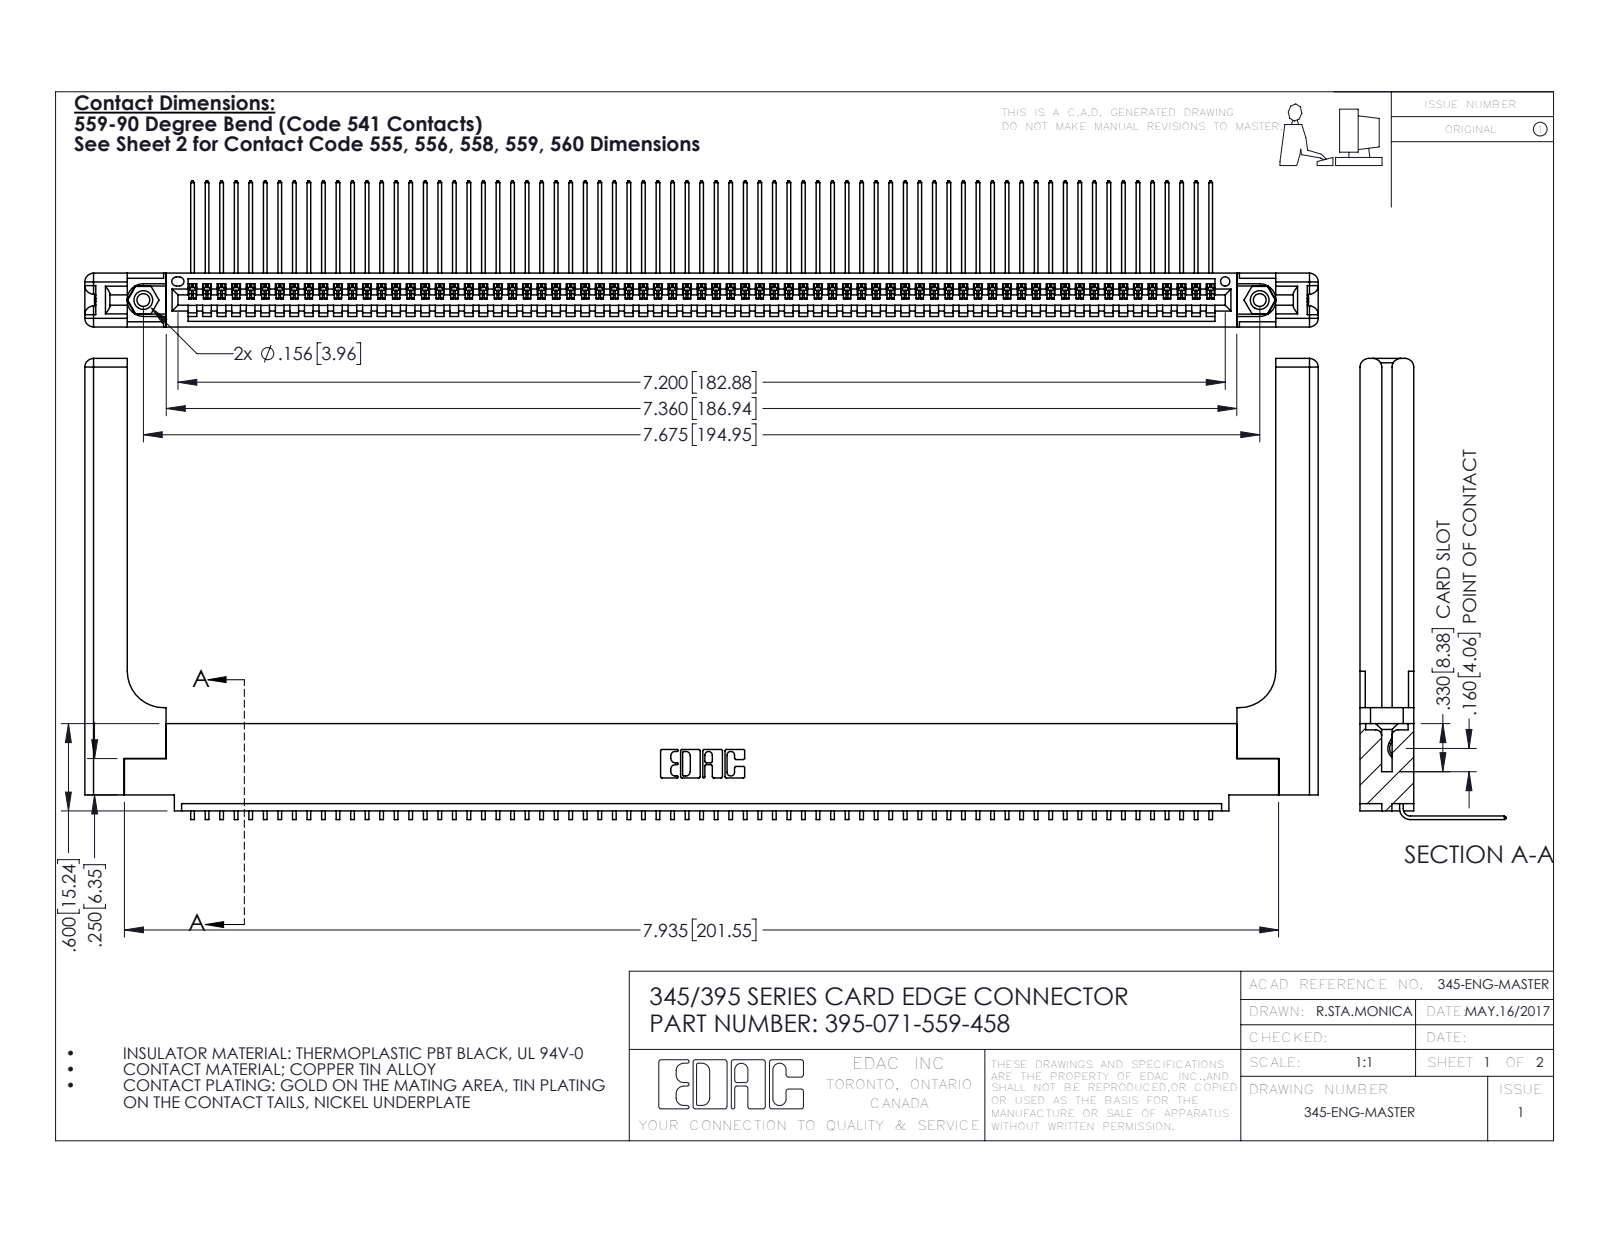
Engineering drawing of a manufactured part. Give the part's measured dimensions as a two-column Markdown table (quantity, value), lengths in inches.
| quantity | value |
| --- | --- |
| part name | 345-250-001_345-250-001-102; 345-292-001_558 559 Tail - 1; 345 Part_0.110 Offset - 0.156 Dia-TH; 345-220-058_345-220-058 (+1 more) |
| STEP written by | SolidWorks 2016 (CONFIG_CONTROL_DESIGN) |
| units | inches |
| bodies | 76 solids, 4646 faces (3214 planar, 1372 cylindrical, 60 other) |
| overall size | 8.479 × 3.169 × 1.005 |
| volume | 1.792 in³ |
| surface area | 54.08 in² |
| round holes (diameter × count) | 0.089 × 2, 0.125 × 2, 0.156 × 2, 0.064 × 1 |
| round bosses / shafts (diameter × count) | 0.155 × 2 |
| partial cylindrical surfaces (radius × count) | 0.006 × 142, 0.01 × 22, 0.06 × 16, 0.007 × 6, 0.031 × 6, 0.026 × 3, 0.03 × 2, 0.031 × 2 |
| main face-to-face distances | 0.072, 0.37, 0.298, 0.098, 0.272, 0.025, 0.2, 0.225, 0.148, 0.15 |
| hole center spacings | 0.27, 7.439, 7.675 |
